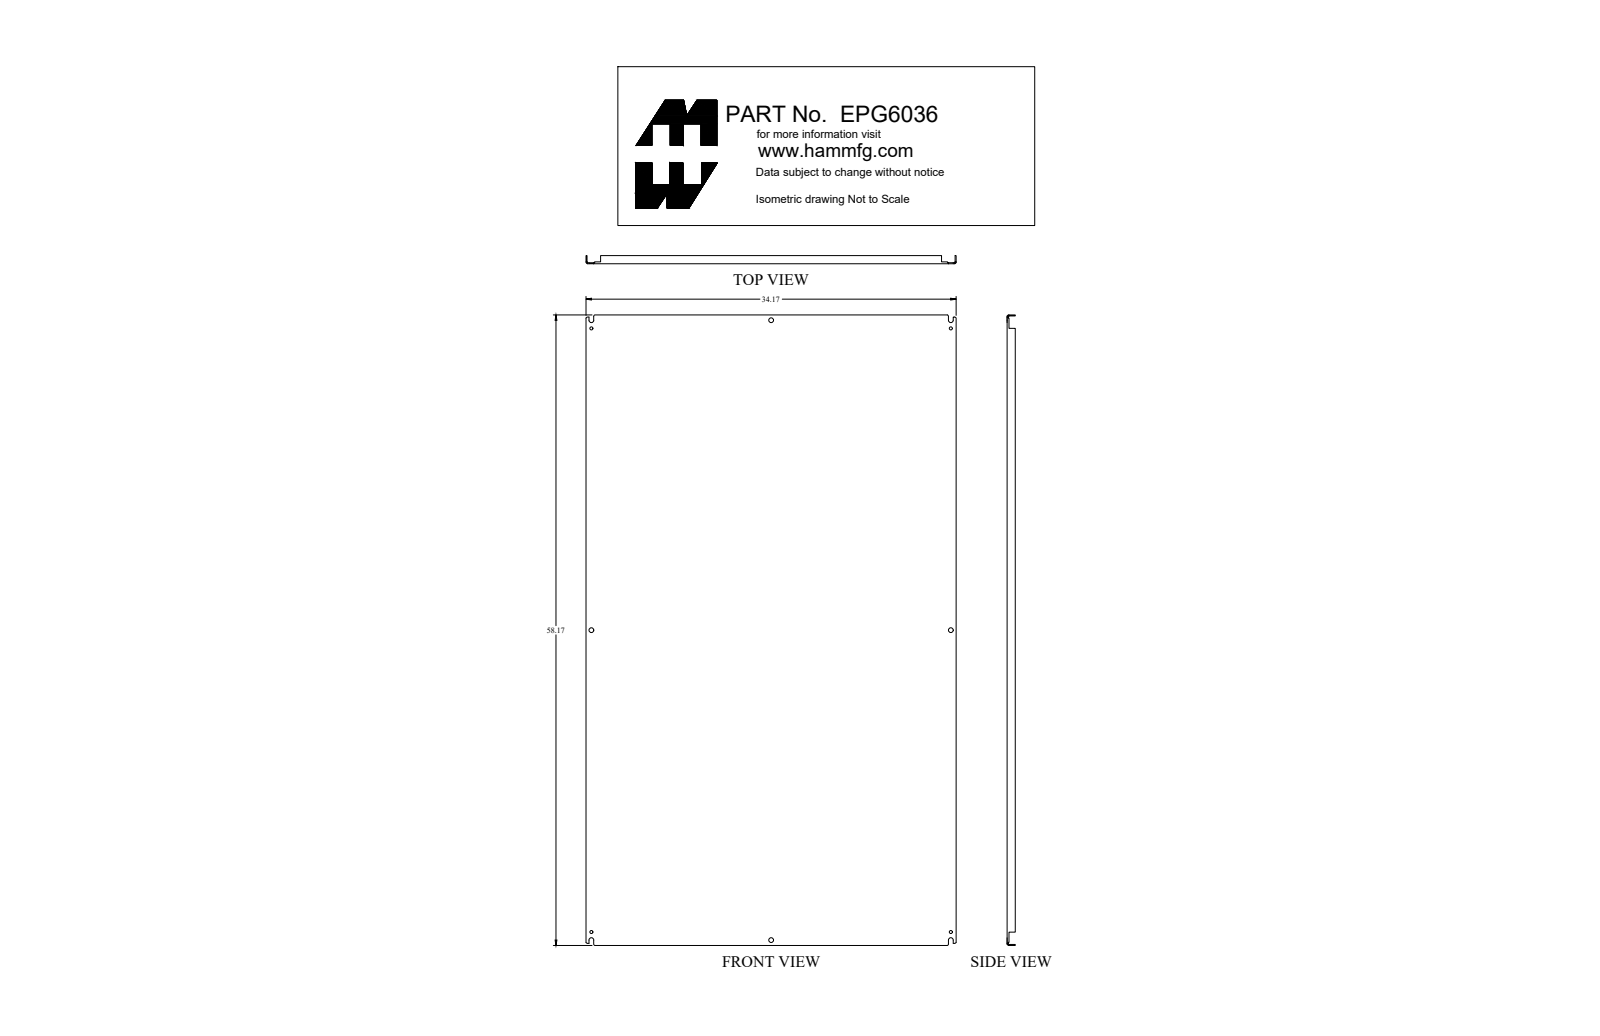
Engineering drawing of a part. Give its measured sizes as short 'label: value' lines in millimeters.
name: EPG6036
written by: SolidWorks 2018 (AUTOMOTIVE_DESIGN)
unit: mm
bodies: 1 solid, 136 faces (74 planar, 46 cylindrical, 16 other)
size: 1477.5 × 867.9 × 19.1
volume: 3 258 000 mm³; area: 2 712 000 mm²
holes: 4× ⌀7.1, 4× ⌀11.1
rounds: 4× R1.2, 4× R1.6, 4× R3.6, 4× R5.6
face distances: 2.4, 865.5, 1475.1, 867.9, 863.1, 1472.7, 1477.5, 19.1, 16.6, 4.3
hole spacings: 421.9, 707.2, 839.7, 1100.4, 1494.2, 843, 1414.5, 1646.6
